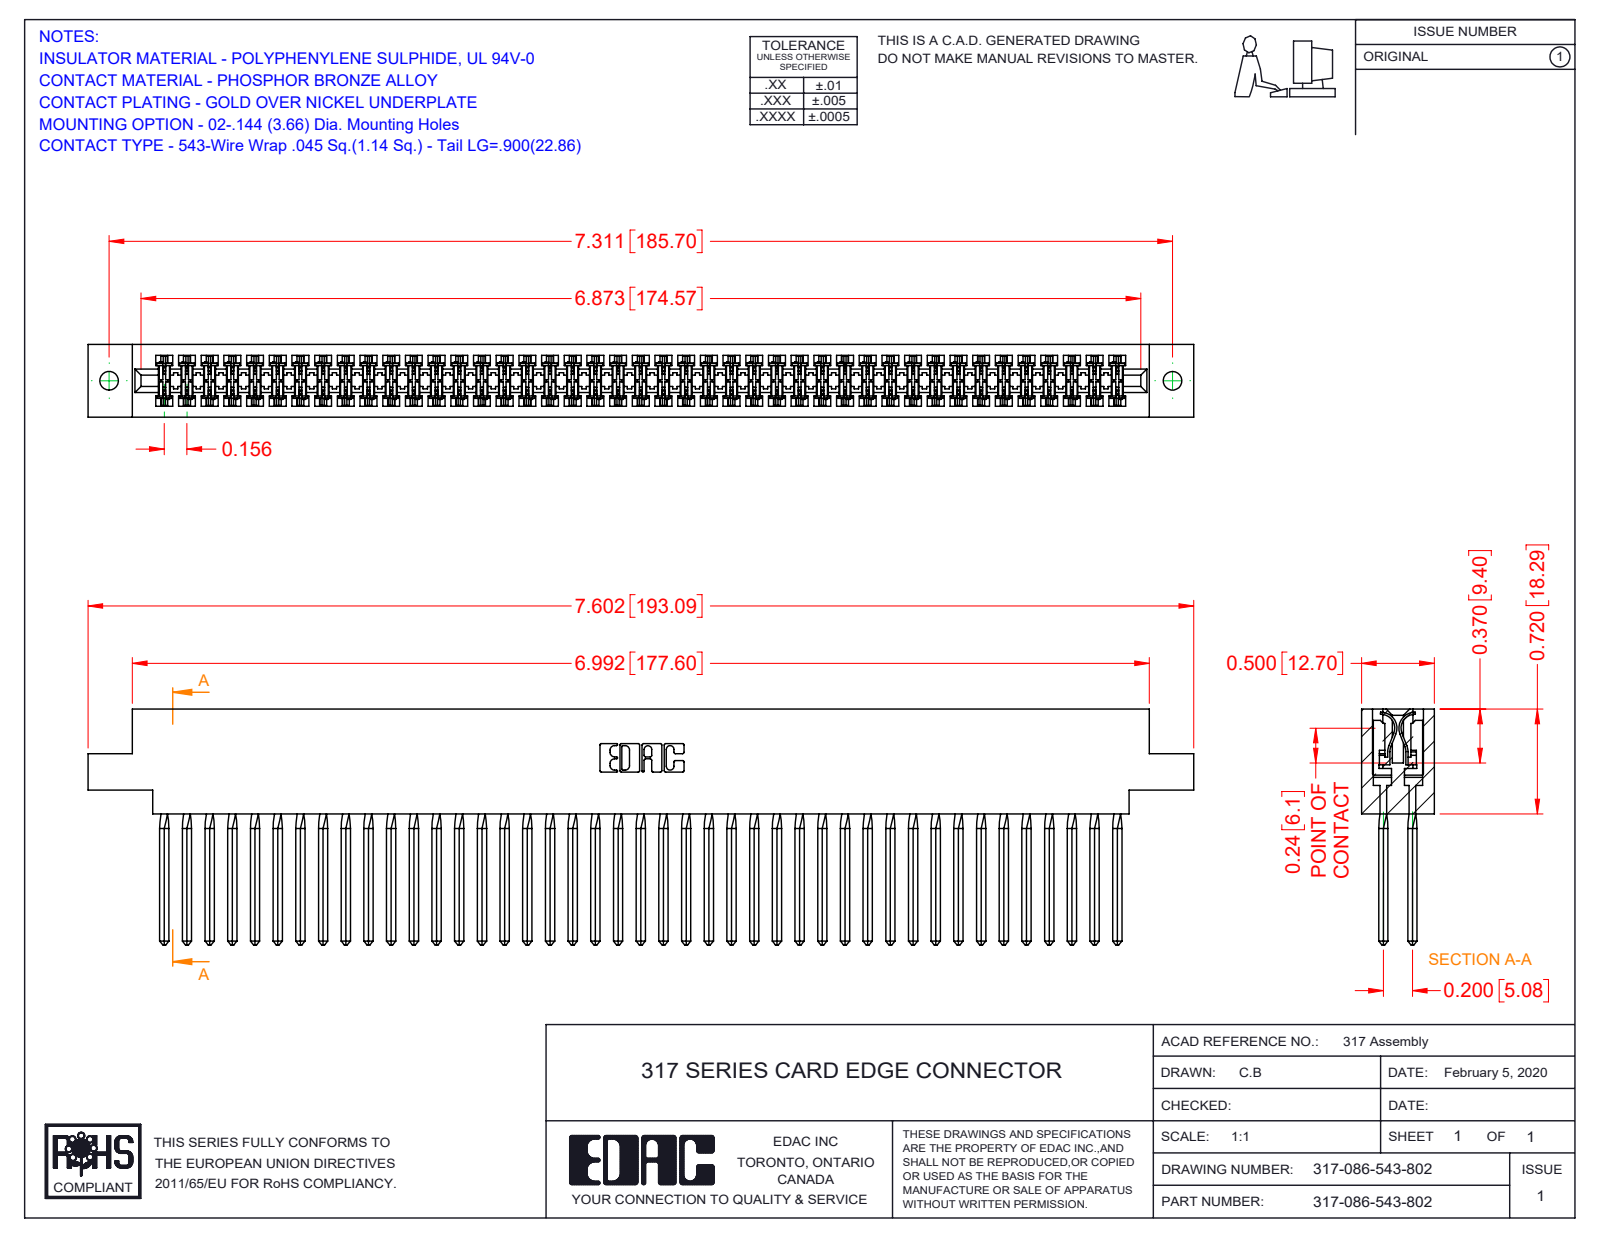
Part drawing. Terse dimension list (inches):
name: 317 Part_.144 Dia; 317-290-001_543; 317-086-543-802
written by: SolidWorks 2016 (CONFIG_CONTROL_DESIGN)
unit: in
bodies: 87 solids, 7756 faces (6336 planar, 1076 cylindrical, 344 other)
size: 7.602 × 1.62 × 0.5
volume: 2.004 in³; area: 76.85 in²
holes: 2× ⌀0.128
rounds: 172× R0.015, 22× R0.01, 6× R0.007, 6× R0.031, 3× R0.026, 2× R0.095, 2× R0.1, 2× R0.11
face distances: 0.5, 0.075, 0.425, 0.35, 0.195, 0.11, 0.094, 0.2, 0.115, 0.131
hole spacings: 7.311
